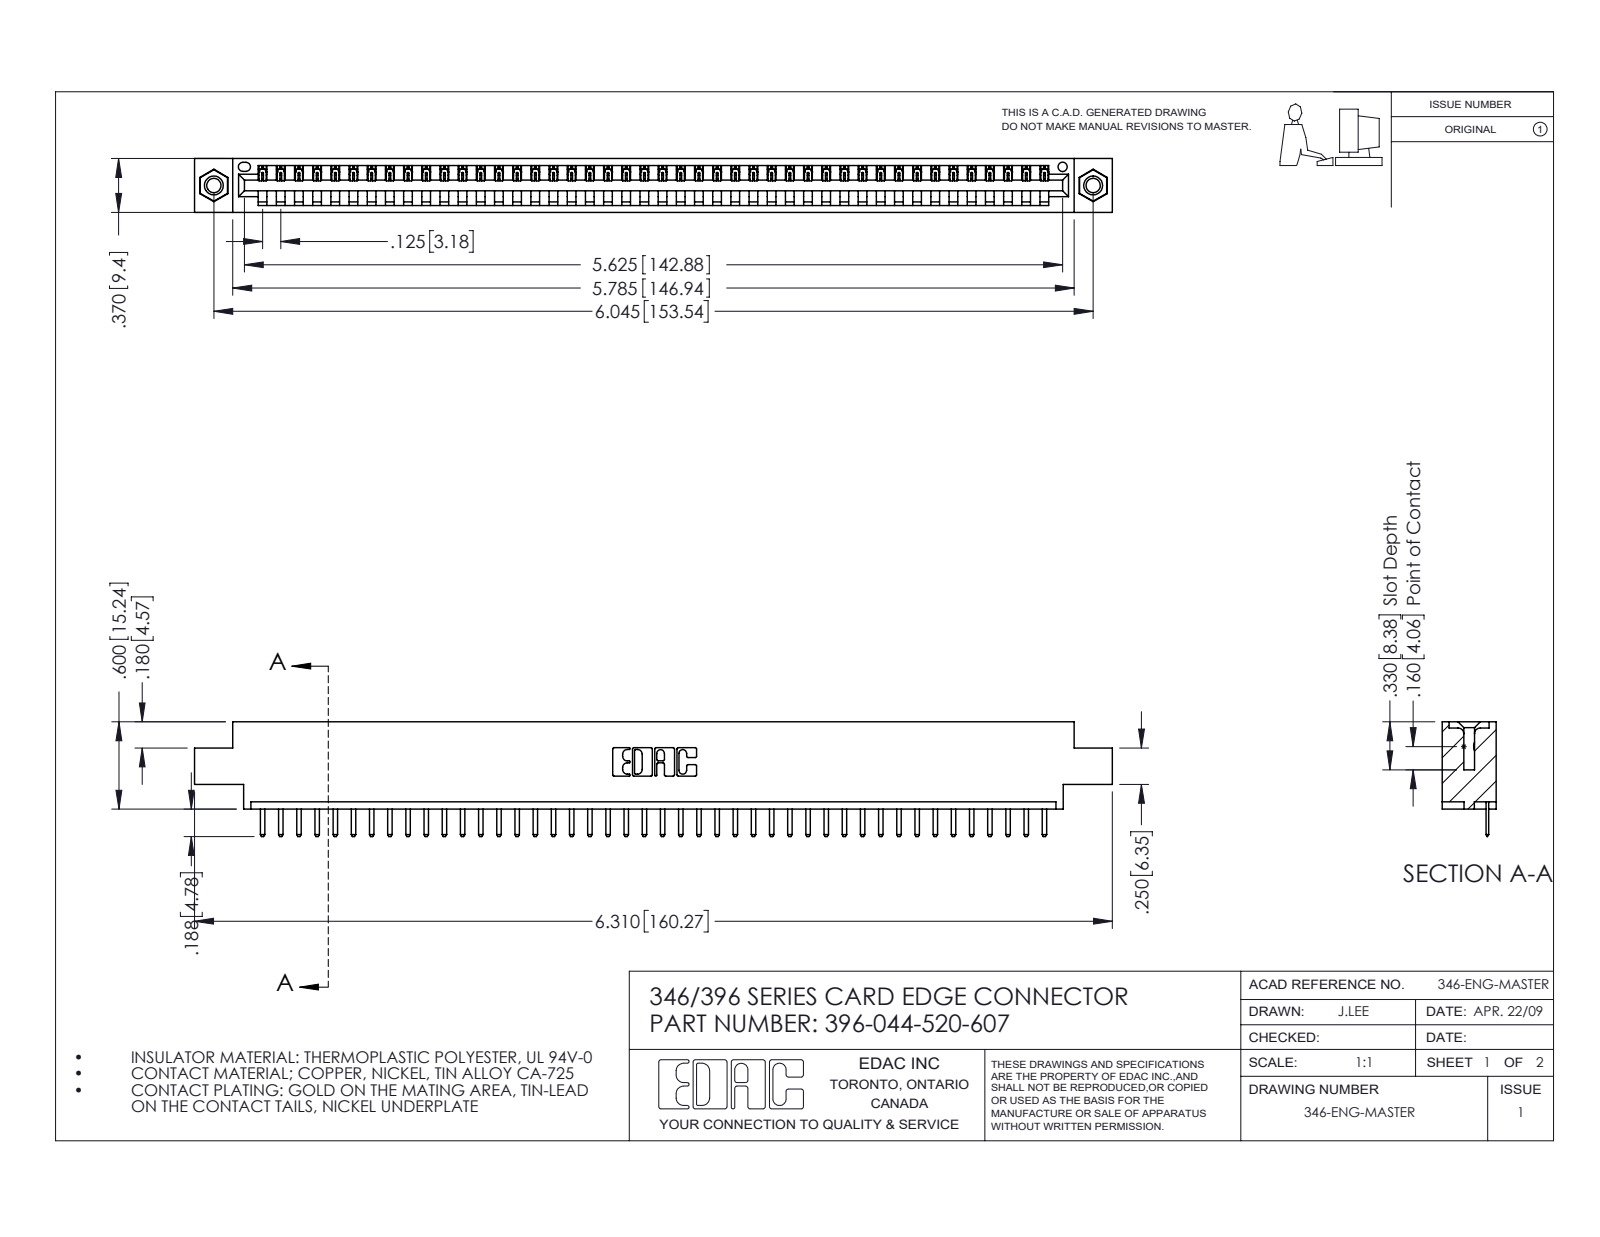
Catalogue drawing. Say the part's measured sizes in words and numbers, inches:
The part is named "345-292-001_345-293-120; 396-044-520-607; 345-250-001_345-250-005-103; 346 Part_0.170 Offset - 0.156 Dia-TI". Its 3-D file was written by "SolidWorks 2016 (CONFIG_CONTROL_DESIGN)". It is 47 solids with 2914 faces: 1960 planar, 938 cylindrical and 16 other. Overall it measures 6.31 by 0.788 by 0.37 inches. Its volume is 0.919 cubic inches and its surface area 28.86 square inches. Round holes: 2 of diameter 0.098, 2 of diameter 0.125, 2 of diameter 0.156, 1 of diameter 0.064. Round bosses or shafts: 2 of diameter 0.155. Partial cylindrical surfaces (rounded edges, fillets, slot ends): 90 of radius 0.01, 88 of radius 0.006, 22 of radius 0.01, 6 of radius 0.007, 6 of radius 0.031, 3 of radius 0.026, 2 of radius 0.031, 2 of radius 0.04. The main face-to-face distances are 0.048, 0.322, 0.37, 0.25, 0.222, 0.148, 0.1, 0.174, 0.072, 0.298. The hole center spacings are 0.246, 5.836, 6.045.
